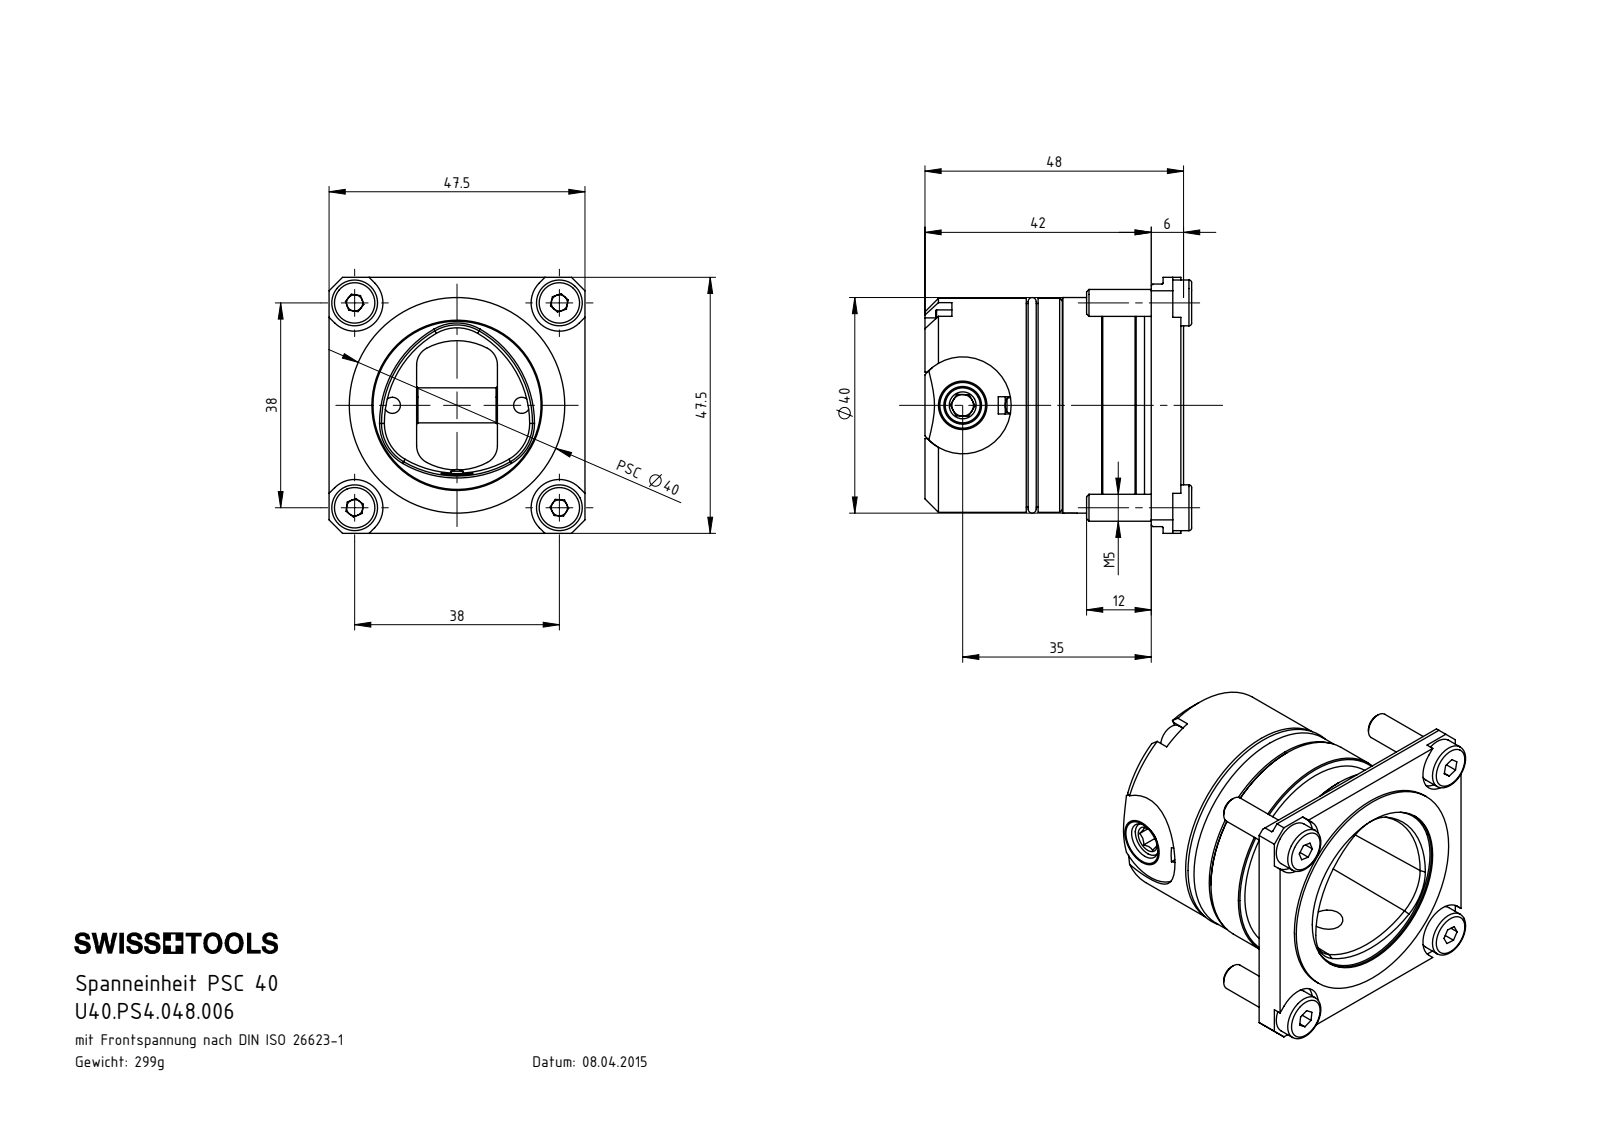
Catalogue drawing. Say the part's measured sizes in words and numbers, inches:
The part is named "DIN 6325_ø2.5x8_2x6; U40-PS4.ER1.036_A; PS4-000.001.020_A; PSC_Teil1 (+8 more)". Its 3-D file was written by "SolidWorks 2017 (AUTOMOTIVE_DESIGN)". It is 19 solids with 605 faces: 308 planar, 101 cylindrical and 196 other. Overall it measures 2.768 by 1.87 by 1.87 inches. Its volume is 5.086 cubic inches and its surface area 57 square inches. Round holes: 4 of diameter 0.217, 3 of diameter 0.13, 2 of diameter 0.118, 2 of diameter 0.157, 1 of diameter 0.039, 1 of diameter 0.098, 1 of diameter 0.165, 1 of diameter 0.181, 1 of diameter 0.276, 1 of diameter 0.492, 1 of diameter 0.709, 1 of diameter 1.244. Round bosses or shafts: 4 of diameter 0.335, 4 of diameter 0.197, 2 of diameter 0.217, 2 of diameter 0.118, 1 of diameter 1.575, 1 of diameter 1.563, 1 of diameter 1.488, 1 of diameter 0.787. Partial cylindrical surfaces (rounded edges, fillets, slot ends): 12 of radius 0.138, 8 of radius 0.012, 4 of radius 0.008, 4 of radius 0.207, 3 of radius 0.118, 2 of radius 0.02, 1 of radius 0.162, 1 of radius 0.354. The main face-to-face distances are 0.945, 0.807, 0.02, 0.787, 0.059, 0.866, 0.728, 1.87, 0.079, 1.024. The hole center spacings are 0.797, 1.058, 1.431, 1.496, 0.472, 0.5, 0.621, 0.649.
